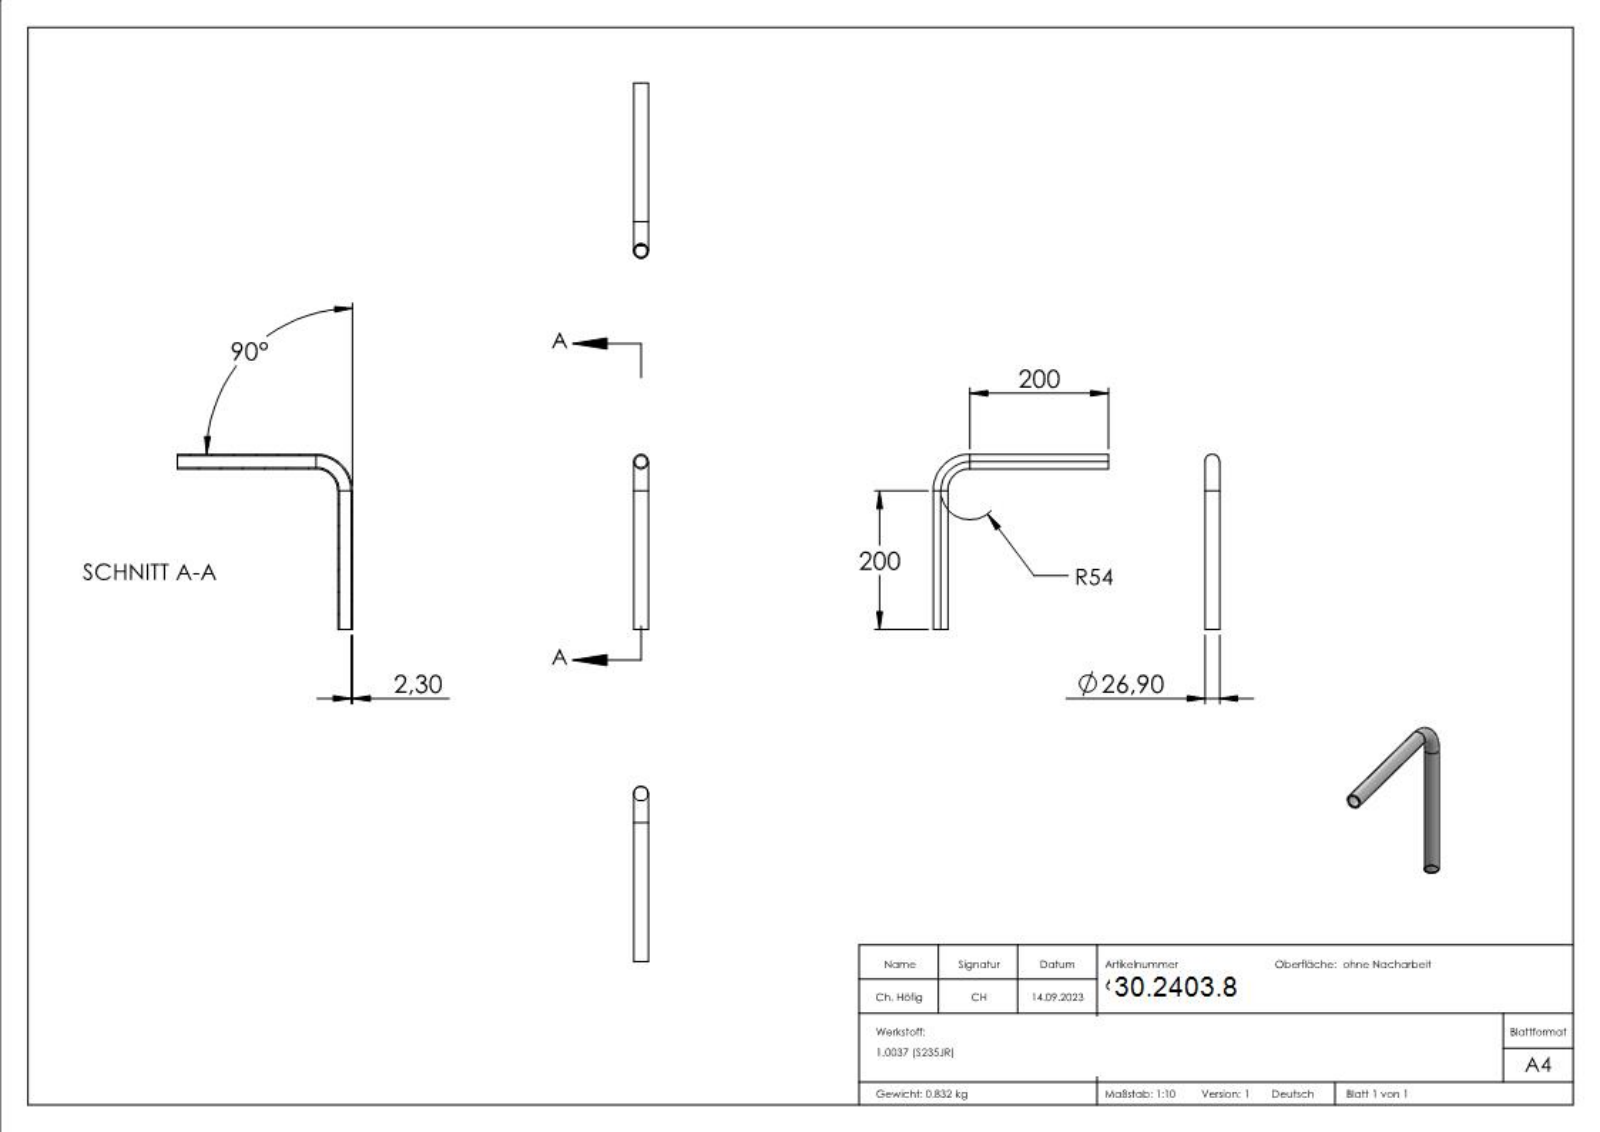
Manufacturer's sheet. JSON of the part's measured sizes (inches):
{"part_name": "6965-090", "step_written_by": "SolidWorks 2018 (CONFIG_CONTROL_DESIGN)", "units": "inches", "bodies": {"solids": 1, "faces": 219, "planar": 103, "cylindrical": 4, "other": 112}, "overall_size": [12.797, 12.797, 1.059], "volume_in3": 6.508, "surface_area_in2": 144.3, "round_holes": [[0.878, 2]], "round_bosses_or_shafts": [[1.059, 2]], "face_to_face_distances": [0.021, 0.023, 0.013, 0.015, 0.013, 0.019, 0.012, 0.014, 0.016, 0.021]}
